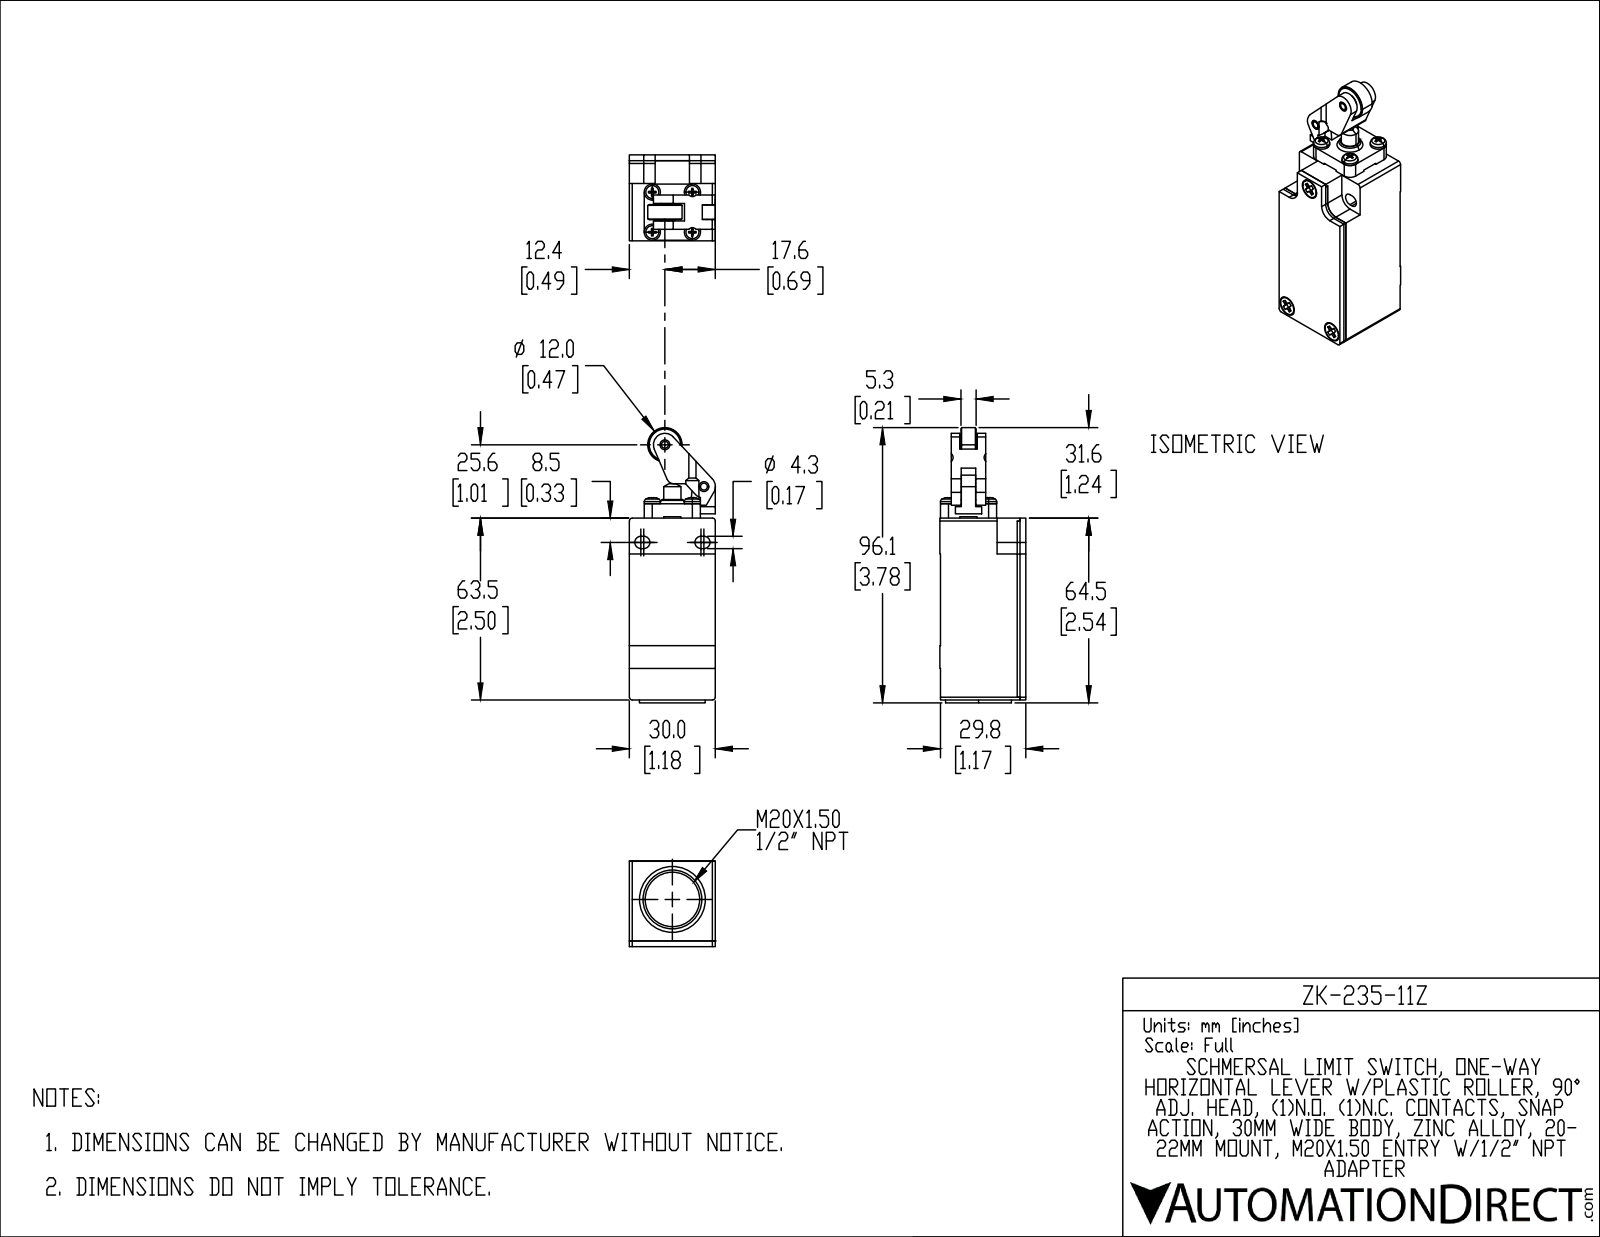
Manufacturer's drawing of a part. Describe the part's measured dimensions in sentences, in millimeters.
The part is named "ZK-235-11Z". Its 3-D file was written by "SolidWorks 2019 (AUTOMOTIVE_DESIGN)". It is 1 solid with 431 faces: 275 planar, 126 cylindrical and 30 other. Overall it measures 96.1 by 30 by 30 millimeters. Its volume is 57 090 cubic millimeters and its surface area 14 510 square millimeters. Round holes: 3 of diameter 7, 2 of diameter 3.4, 1 of diameter 6.2, 1 of diameter 13, 1 of diameter 13.8, 1 of diameter 19. Round bosses or shafts: 4 of diameter 5.6, 4 of diameter 5.4, 3 of diameter 6.5, 2 of diameter 2.4, 1 of diameter 23, 1 of diameter 12, 1 of diameter 10.5, 1 of diameter 7. Partial cylindrical surfaces (rounded edges, fillets, slot ends): 12 of radius 0.5, 4 of radius 1, 4 of radius 2.2, 4 of radius 2.8, 4 of radius 4, 3 of radius 2.5, 2 of radius 1.6, 2 of radius 4. The main face-to-face distances are 30, 29.8, 4, 63.5, 16, 3.8, 15.8, 12, 0.5, 9. The hole center spacings are 56.6, 3.5, 18.6, 19.9, 22, 29.7, 70.5, 73.8.
